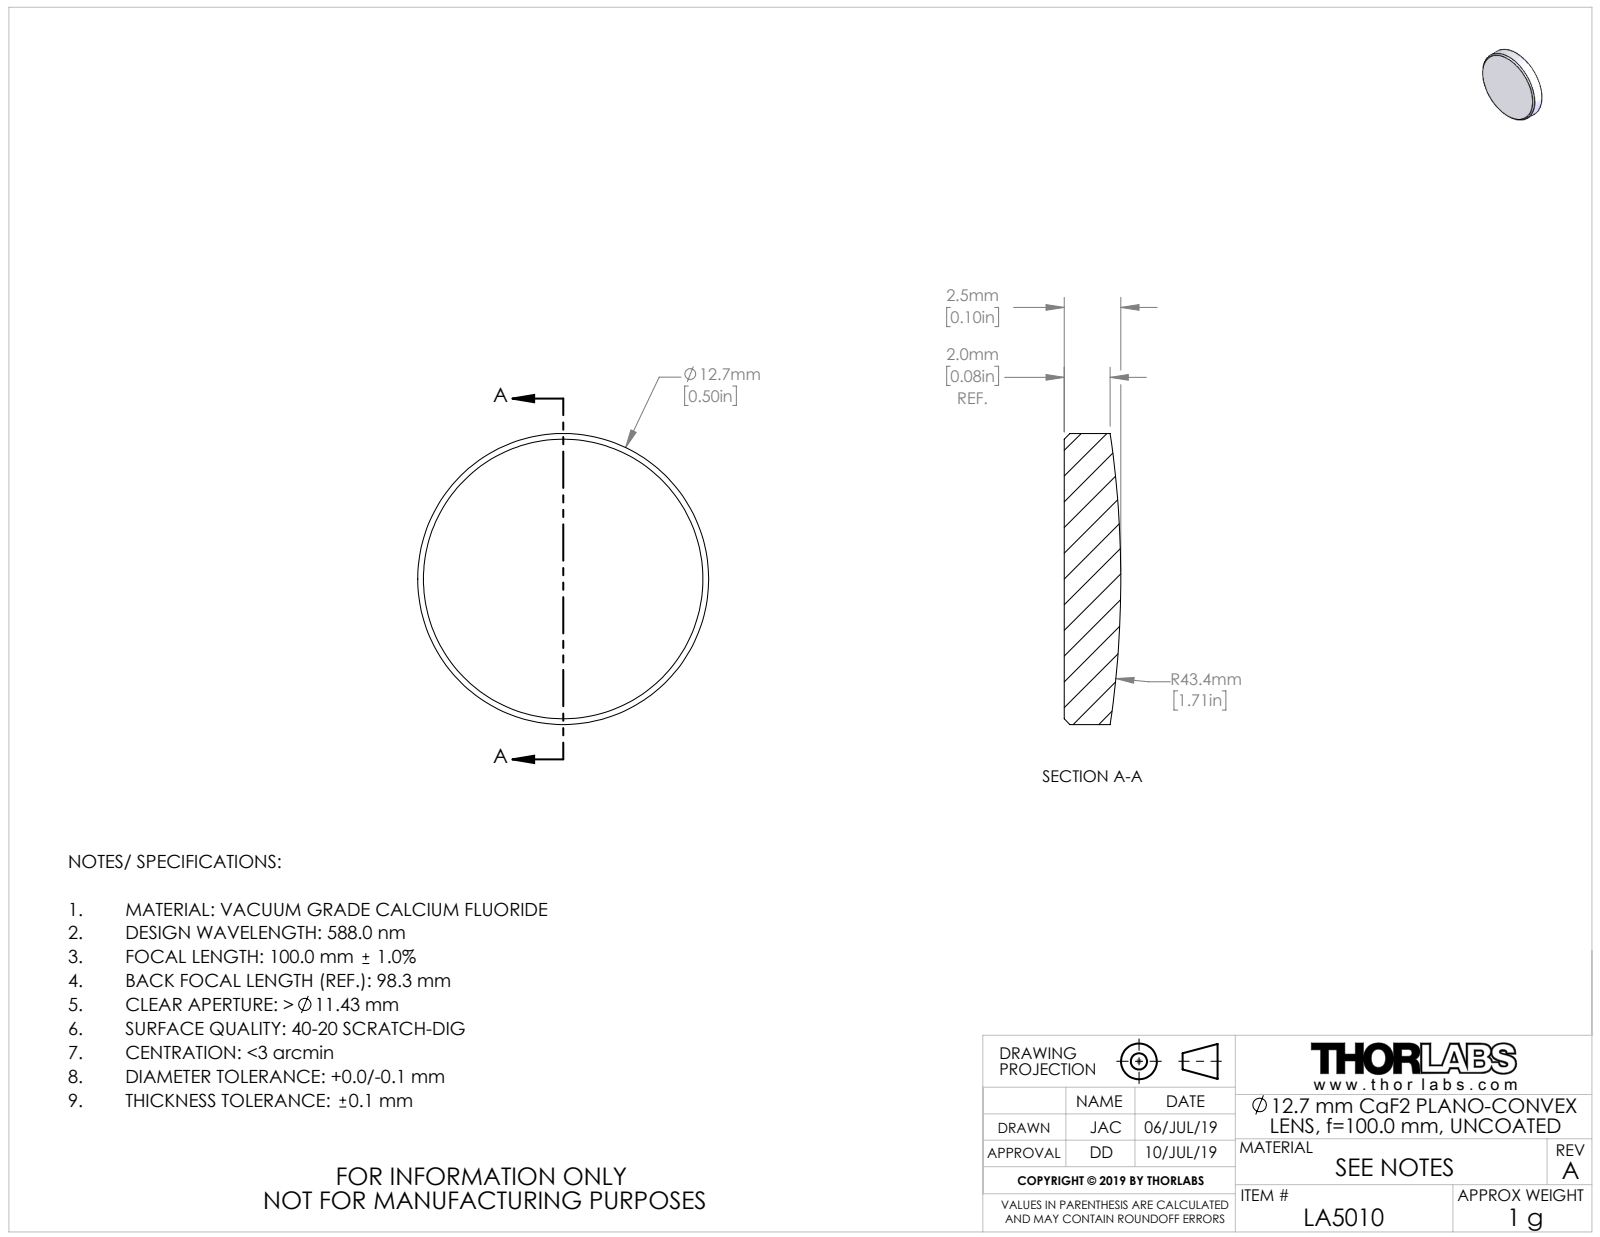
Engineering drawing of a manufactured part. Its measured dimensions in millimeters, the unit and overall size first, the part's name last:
Units: millimetres
Overall size (bounding box): 12.7 × 12.7 × 2.47
Round bosses / shafts (diameter × count): ⌀12.7 ×1
Volume: 282 mm³ · Surface area: 328 mm²
Bodies: 1 solid, 7 faces (1 planar, 2 cylindrical, 4 other)
Part name (STEP PRODUCT): TTN188114-E0W
STEP written by: SolidWorks 2018 (CONFIG_CONTROL_DESIGN)
